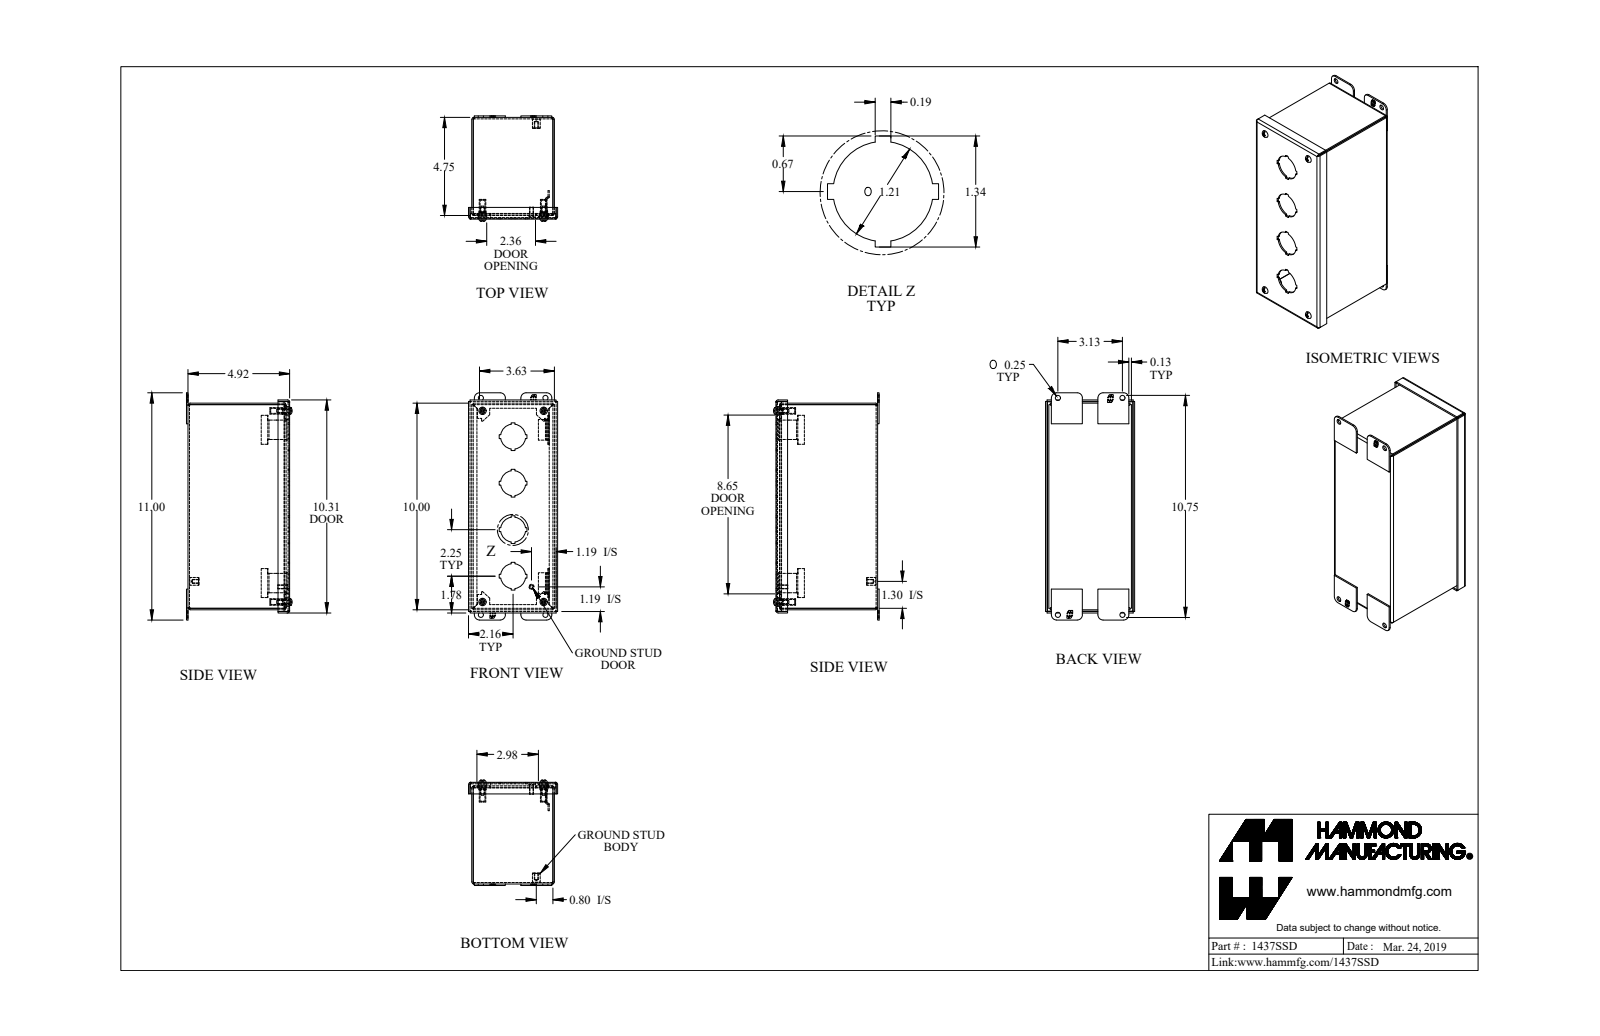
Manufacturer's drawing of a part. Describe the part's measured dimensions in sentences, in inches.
The part is named "1437SSD_Default". Its 3-D file was written by "SolidWorks 2019 (CONFIG_CONTROL_DESIGN)". It is 23 solids with 669 faces: 471 planar, 168 cylindrical and 30 other. Overall it measures 11 by 5.104 by 4.312 inches. Its volume is 19.98 cubic inches and its surface area 533.7 square inches. Round holes: 8 of diameter 0.25, 4 of diameter 0.065, 4 of diameter 0.239, 4 of diameter 0.253, 4 of diameter 0.406, 4 of diameter 1.21, 1 of diameter 0.156. Round bosses or shafts: 5 of diameter 0.19, 4 of diameter 0.406, 4 of diameter 0.315, 4 of diameter 0.148, 1 of diameter 0.375, 1 of diameter 0.25. Partial cylindrical surfaces (rounded edges, fillets, slot ends): 12 of radius 0.036, 12 of radius 0.108, 8 of radius 0.25, 4 of radius 0.029, 4 of radius 0.086, 4 of radius 0.171, 2 of radius 0.125. The main face-to-face distances are 0.072, 3.928, 4.85, 3.856, 4.922, 4, 4.778, 9.928, 0.156, 4.084. The hole center spacings are 9.25, 9.875, 10.333, 2.961, 3.107, 9.712, 2.962, 0.63.
